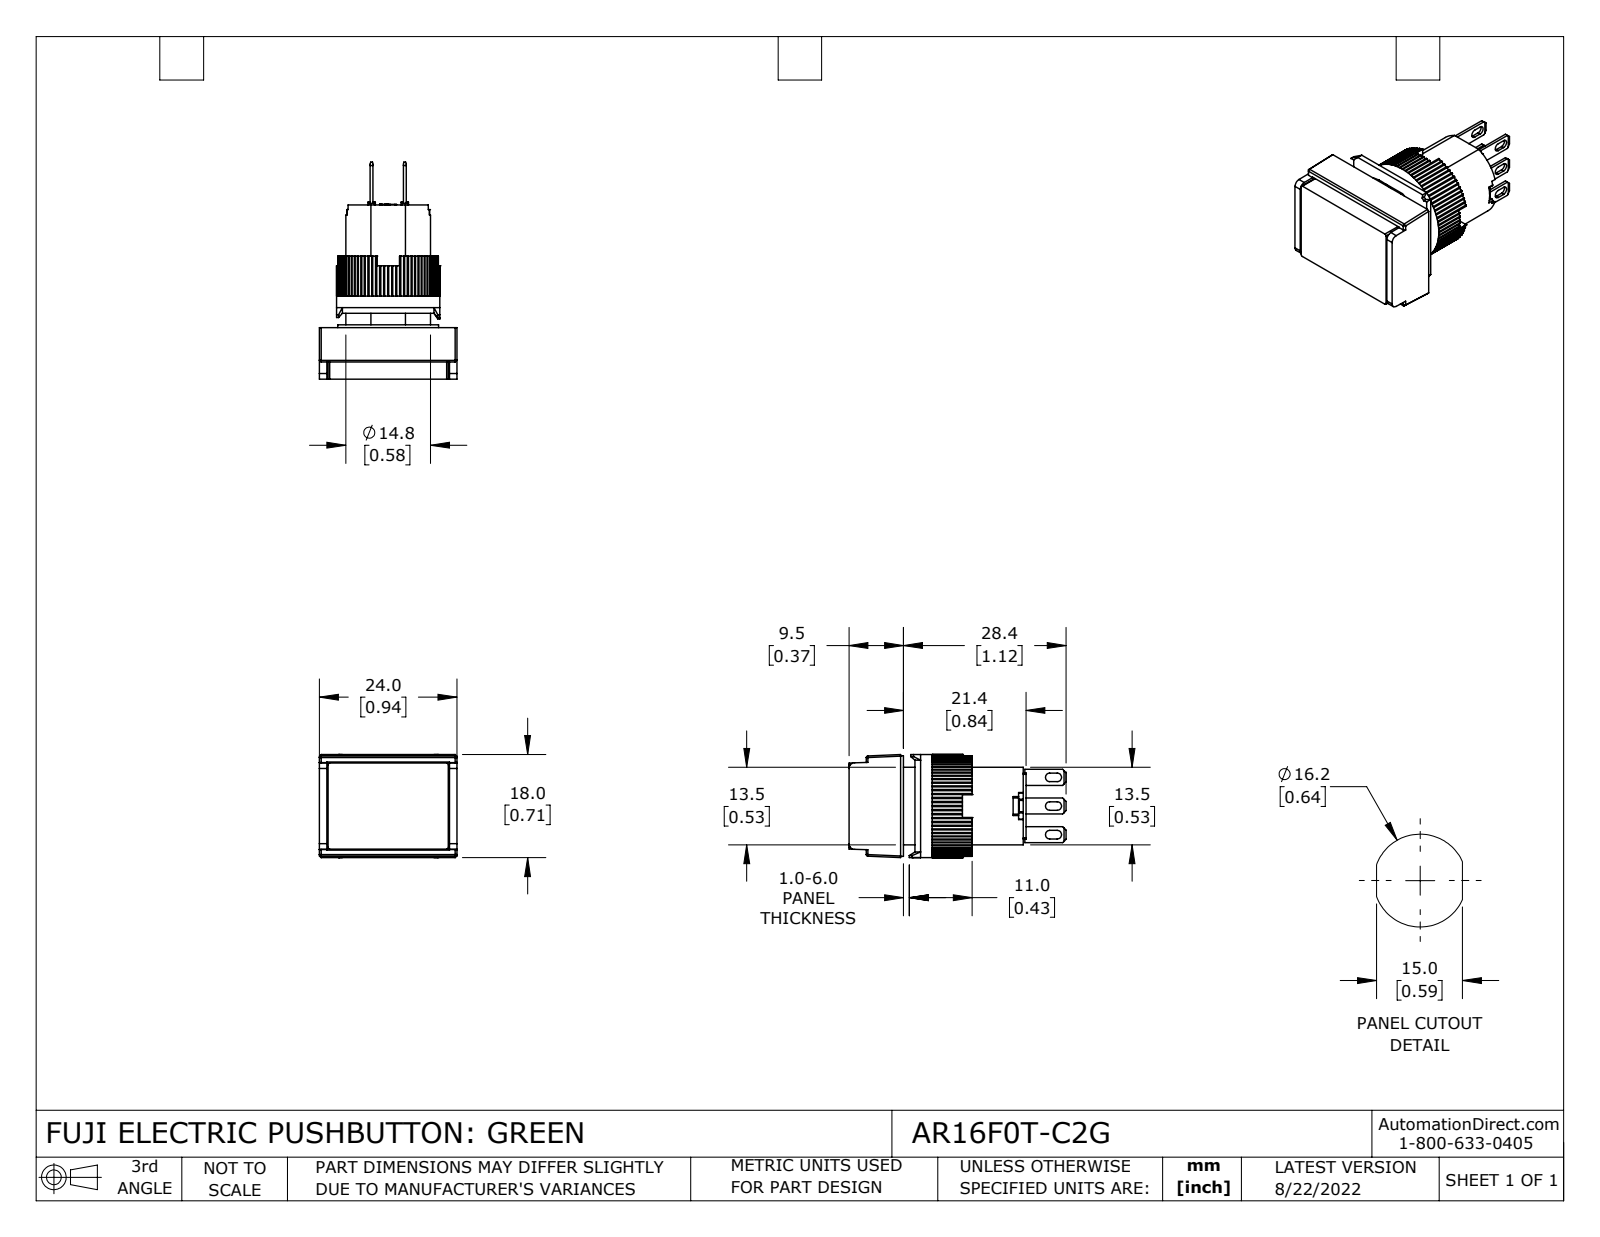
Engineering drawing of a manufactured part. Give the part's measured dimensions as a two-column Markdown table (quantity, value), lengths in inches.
| quantity | value |
| --- | --- |
| part name | AR16F0T-C2G |
| STEP written by | SolidWorks 2021 (CONFIG_CONTROL_DESIGN) |
| units | inches |
| bodies | 12 solids, 813 faces (632 planar, 177 cylindrical, 4 other) |
| overall size | 1.492 × 0.945 × 0.709 |
| volume | 0.443 in³ |
| surface area | 9.124 in² |
| round holes (diameter × count) | 0.543 × 1, 0.583 × 1 |
| round bosses / shafts (diameter × count) | 0.709 × 1, 0.693 × 1 |
| partial cylindrical surfaces (radius × count) | 0.01 × 80, 0.008 × 12, 0.012 × 6, 0.03 × 6, 0.039 × 2 |
| main face-to-face distances | 0.213, 0.354, 0.142, 0.492, 0.35, 0.138, 0.02, 0.843, 0.059, 0.453 |
